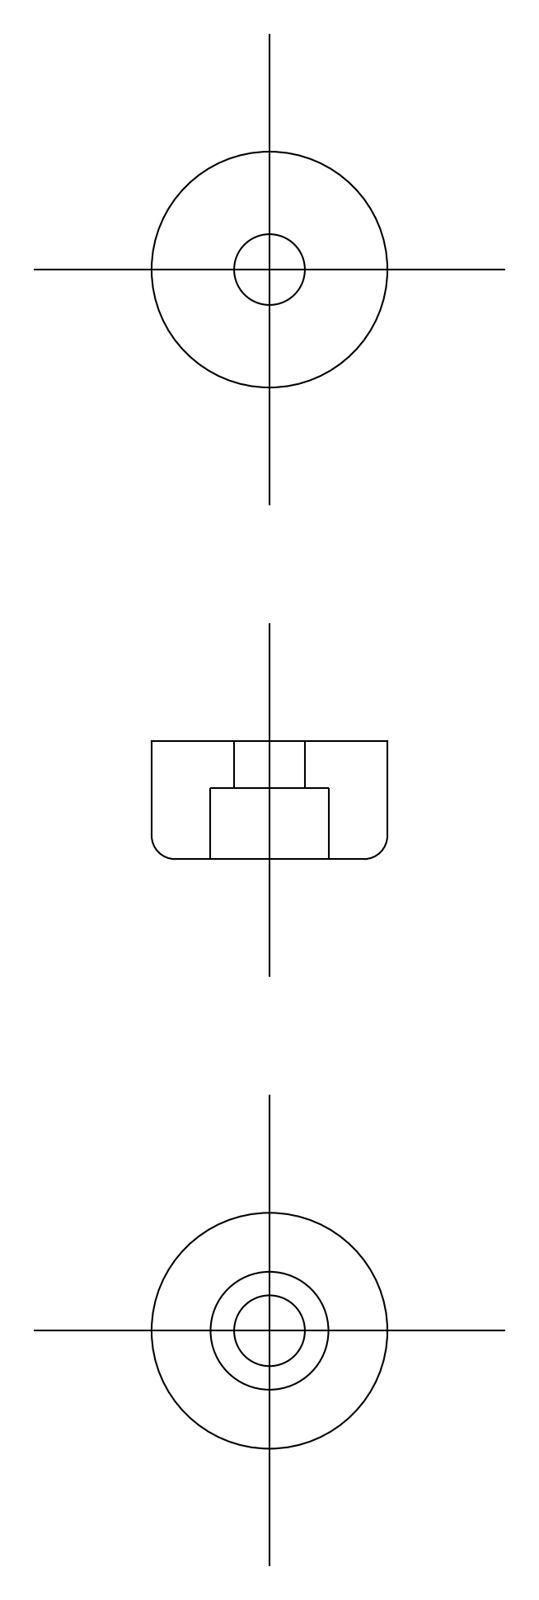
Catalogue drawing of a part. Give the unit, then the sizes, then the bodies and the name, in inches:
Units: inches
Overall size (bounding box): 0.394 × 0.394 × 0.197
Round holes (diameter × count): ⌀0.118 ×1, ⌀0.197 ×1, ⌀0.315 ×1
Round bosses / shafts (diameter × count): ⌀0.394 ×1
Main face-to-face distances: 0.02, 0.079, 0.059, 0.118, 0.138, 0.197
Volume: 0.019 in³ · Surface area: 0.814 in²
Bodies: 2 solids, 20 faces (6 planar, 12 cylindrical, 2 other)
Part name (STEP PRODUCT): washer; rubber foot
STEP written by: spGate 15.6.1 (AUTOMOTIVE_DESIGN)
